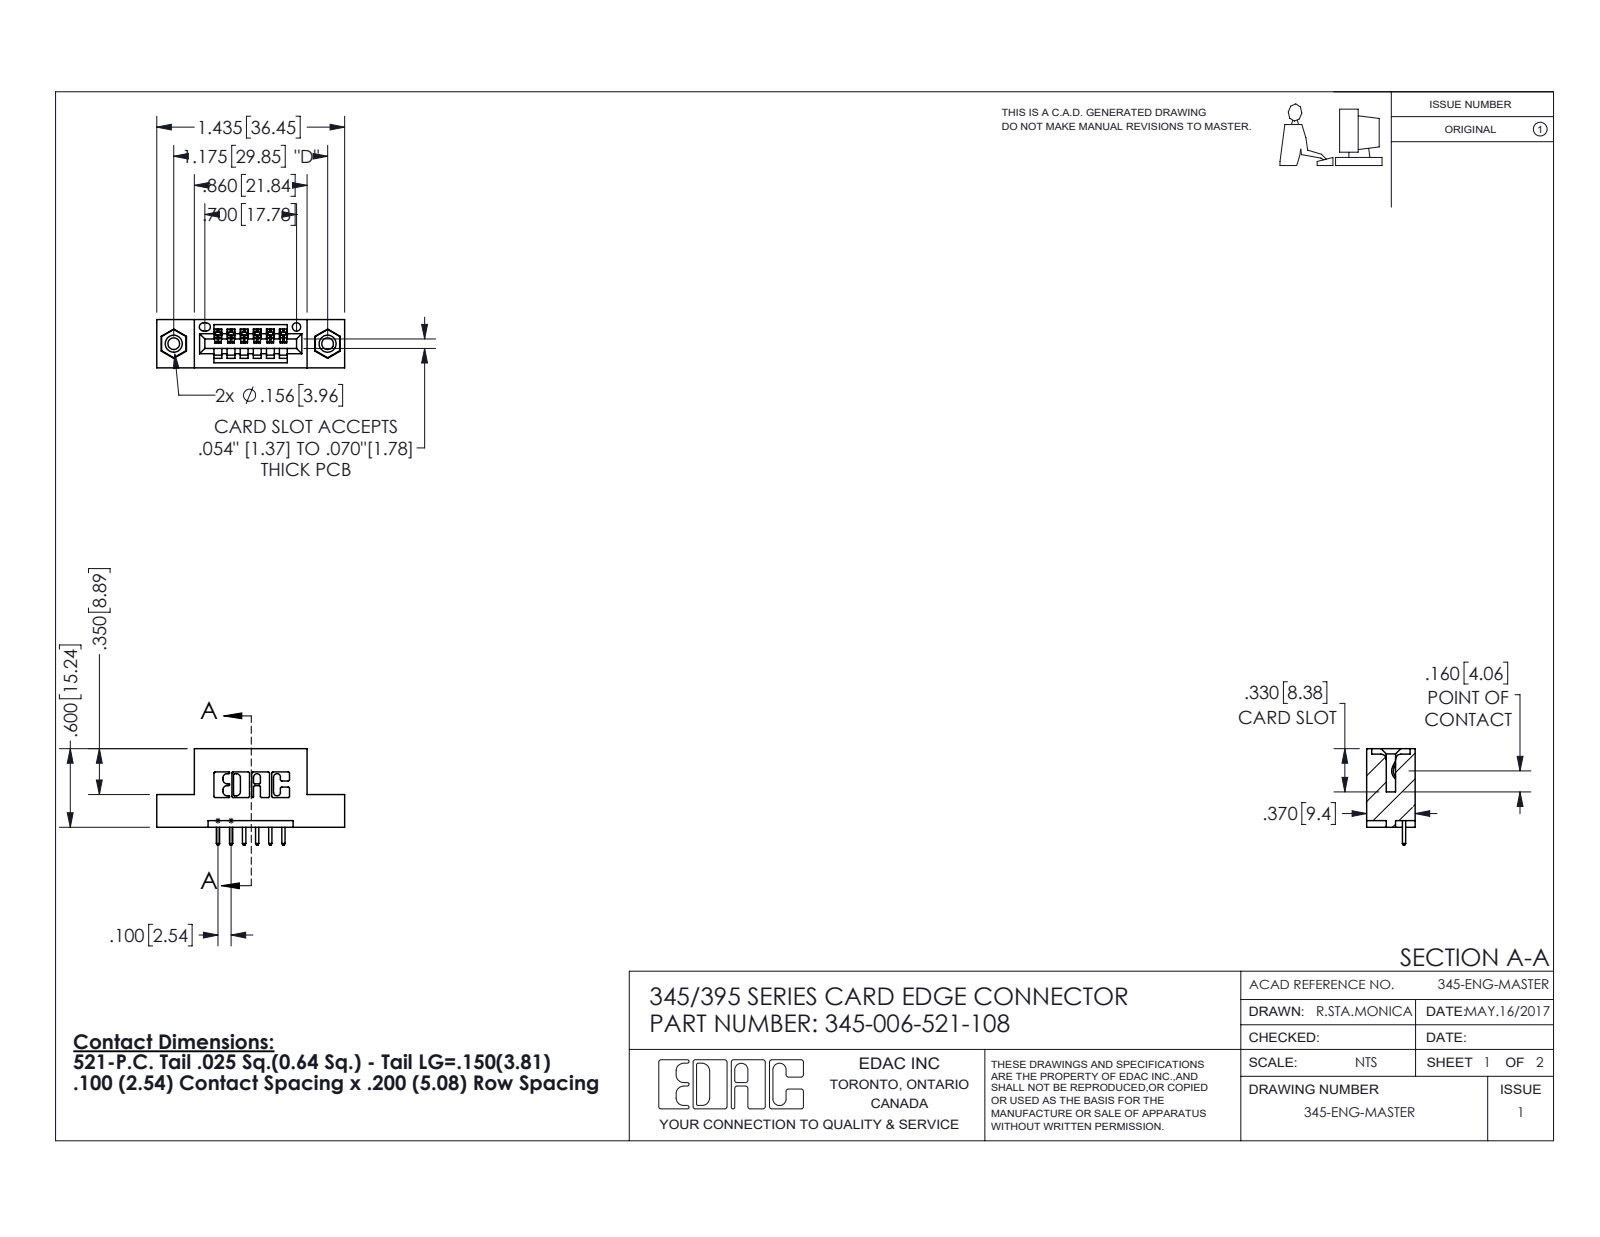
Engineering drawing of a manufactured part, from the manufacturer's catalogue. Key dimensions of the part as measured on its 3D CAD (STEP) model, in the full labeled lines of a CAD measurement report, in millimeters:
Part name (STEP PRODUCT): 345-250-001_345-250-003-102; 345 Part_Flush Mounting Lugs - 0.156 Dia-TI; 345-006-521-108; 345-292-001_345-293-121
STEP written by: SolidWorks 2016 (CONFIG_CONTROL_DESIGN)
Units: millimetres
Bodies: 9 solids, 534 faces (352 planar, 166 cylindrical, 16 other)
Overall size (bounding box): 36.4 × 18.7 × 9.4
Volume: 3 150 mm³ · Surface area: 3 641 mm²
Round holes (diameter × count): ⌀2.3 ×2, ⌀3.2 ×2, ⌀4 ×2, ⌀1.6 ×1
Round bosses / shafts (diameter × count): ⌀3.9 ×2
Partial cylindrical surfaces — rounded edges, fillets, slot ends (radius × count): R0.3 ×22, R0.2 ×12, R0.3 ×12, R0.2 ×6, R0.8 ×6, R0.7 ×3, R0.8 ×2, R1 ×2
Main face-to-face distances: 5.1, 9.4, 1.8, 7.6, 2.5, 0.6, 2.5, 6.9, 1.5, 7.6
Hole centre spacings: 6.9, 24, 29.8
